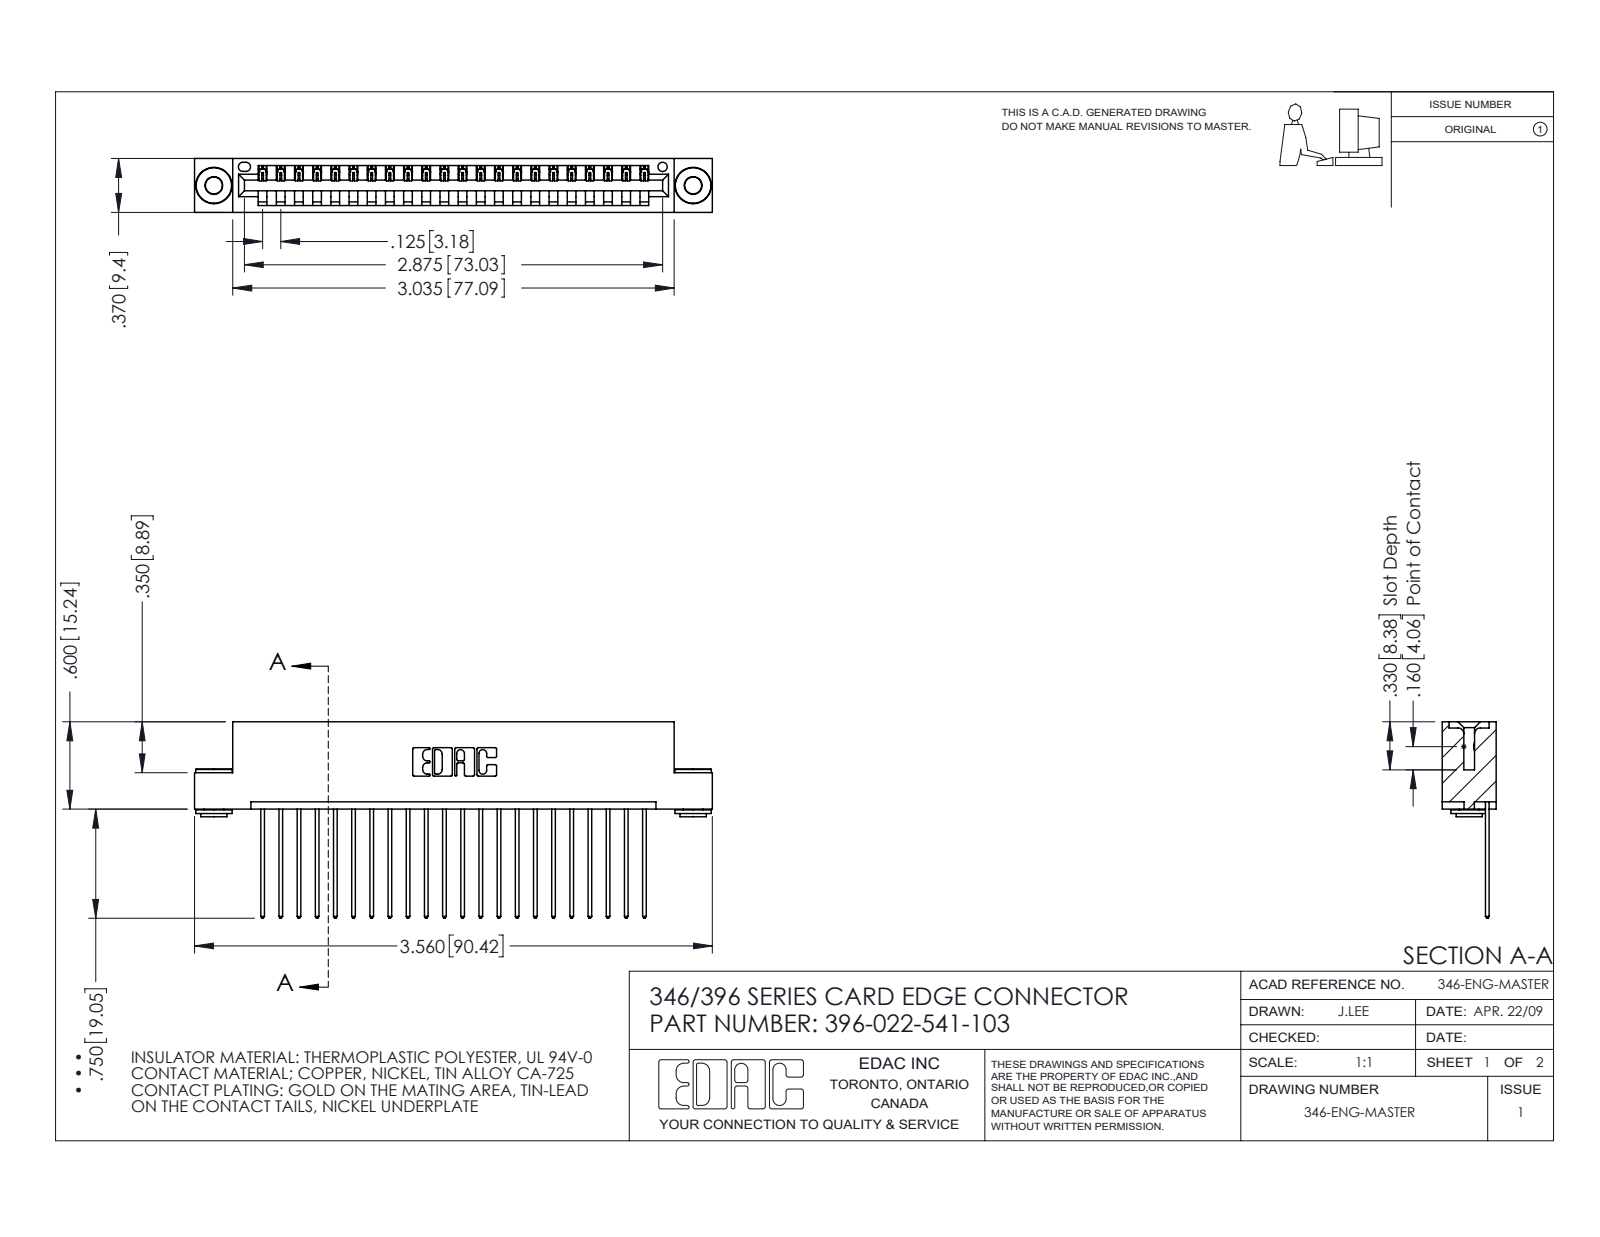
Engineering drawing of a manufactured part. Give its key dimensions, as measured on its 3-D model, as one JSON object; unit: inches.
{"part_name": "345-292-001_345-293-141; 346 Part_Flush Mounting Lugs - 0.156 Dia-TH; 345-250-002_345-250-002-102; 396-022-541-103", "step_written_by": "SolidWorks 2016 (CONFIG_CONTROL_DESIGN)", "units": "inches", "bodies": {"solids": 25, "faces": 1436, "planar": 966, "cylindrical": 462, "other": 8}, "overall_size": [3.56, 1.35, 0.37], "volume_in3": 0.525, "surface_area_in2": 17.36, "round_holes": [[0.116, 2], [0.156, 2], [0.064, 1]], "round_bosses_or_shafts": [[0.25, 2], [0.18, 2], [0.136, 2]], "partial_cylinders_radius": [[0.006, 44], [0.01, 44], [0.01, 22], [0.007, 6], [0.031, 6], [0.026, 3], [0.031, 2], [0.04, 2]], "face_to_face_distances": [0.048, 0.322, 0.25, 0.37, 0.025, 0.072, 0.298, 0.148, 0.222, 0.1], "hole_center_spacings": [0.246, 3.087, 3.295]}
